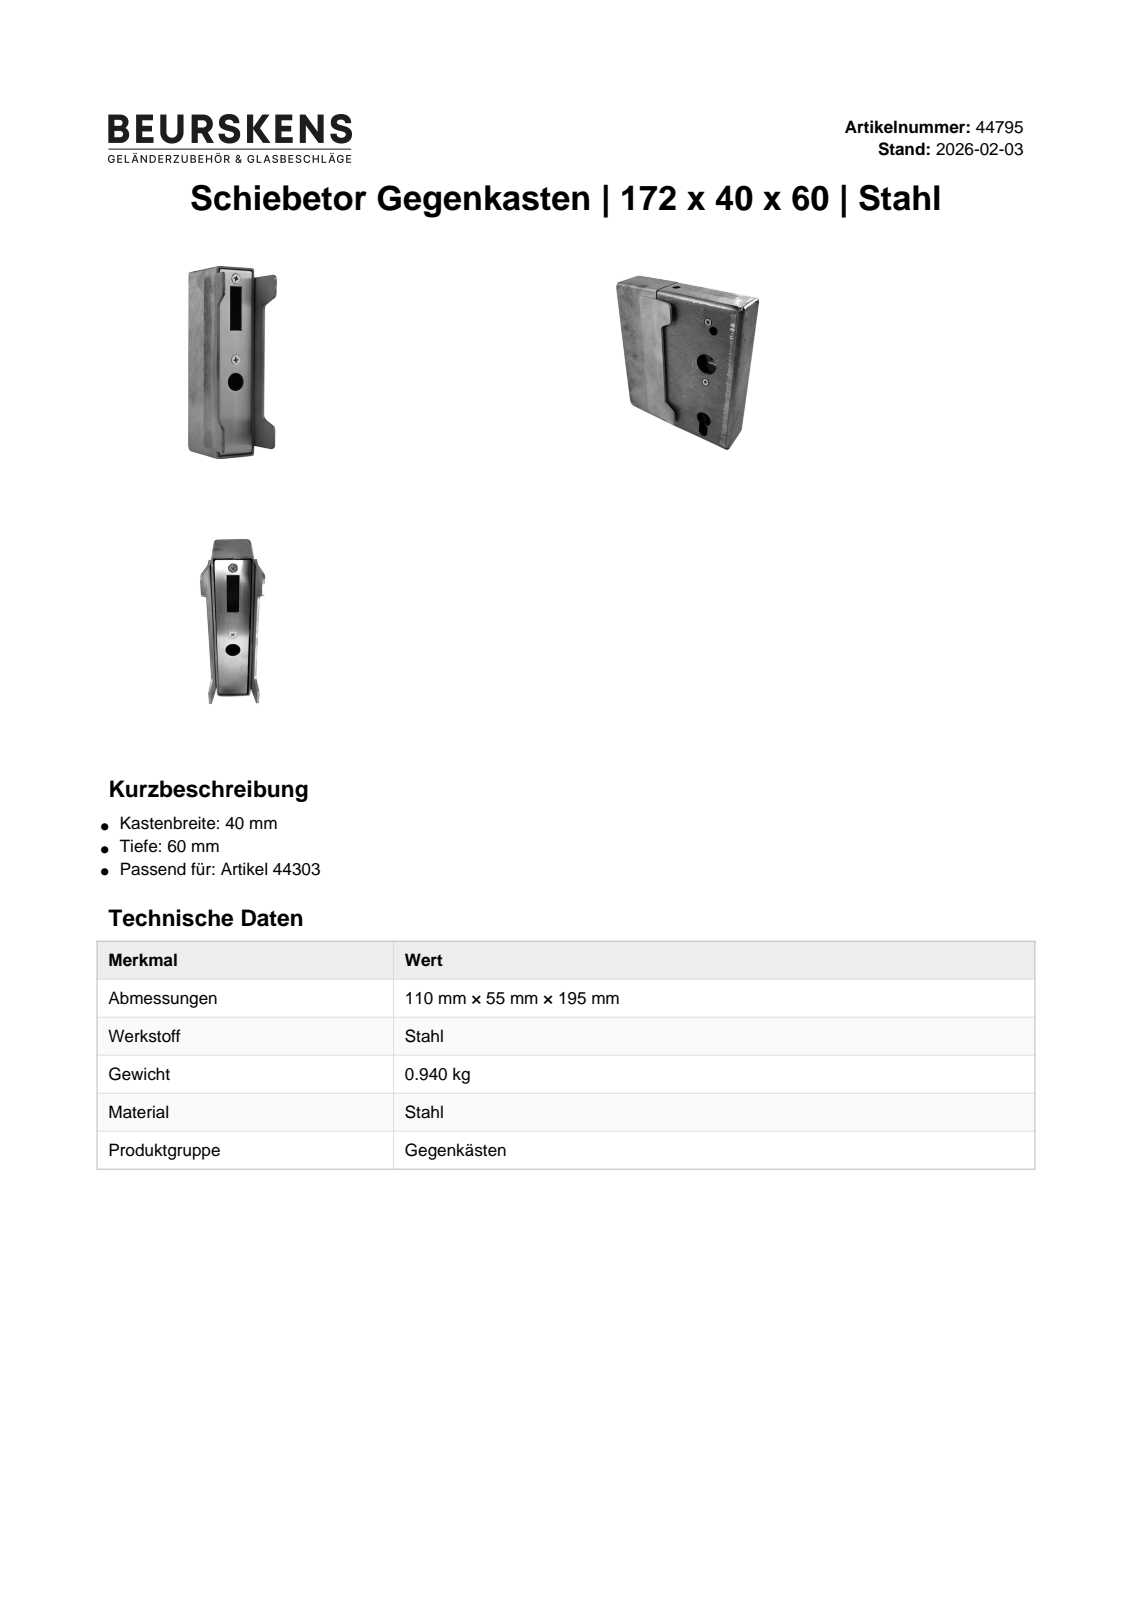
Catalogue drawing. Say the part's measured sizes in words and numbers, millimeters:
The part is named "41529; 40944; 41535; 44795". Its 3-D file was written by "SolidWorks 2020 (CONFIG_CONTROL_DESIGN)". It is 4 solids with 148 faces: 82 planar, 58 cylindrical and 8 other. Overall it measures 172 by 85 by 54.82 millimeters. Its volume is 125 747 cubic millimeters and its surface area 99 148 square millimeters. Round holes: 2 of diameter 4.2, 2 of diameter 5.5, 2 of diameter 6, 1 of diameter 6.5, 1 of diameter 16. Round bosses or shafts: 2 of diameter 5. Partial cylindrical surfaces (rounded edges, fillets, slot ends): 8 of radius 4, 8 of radius 5, 4 of radius 2. The main face-to-face distances are 2.5, 37.5, 3, 40, 35, 5.5, 40.5, 43, 57.5, 54.5. The hole center spacings are 57.5, 19.75, 72.75, 92.5, 115.
